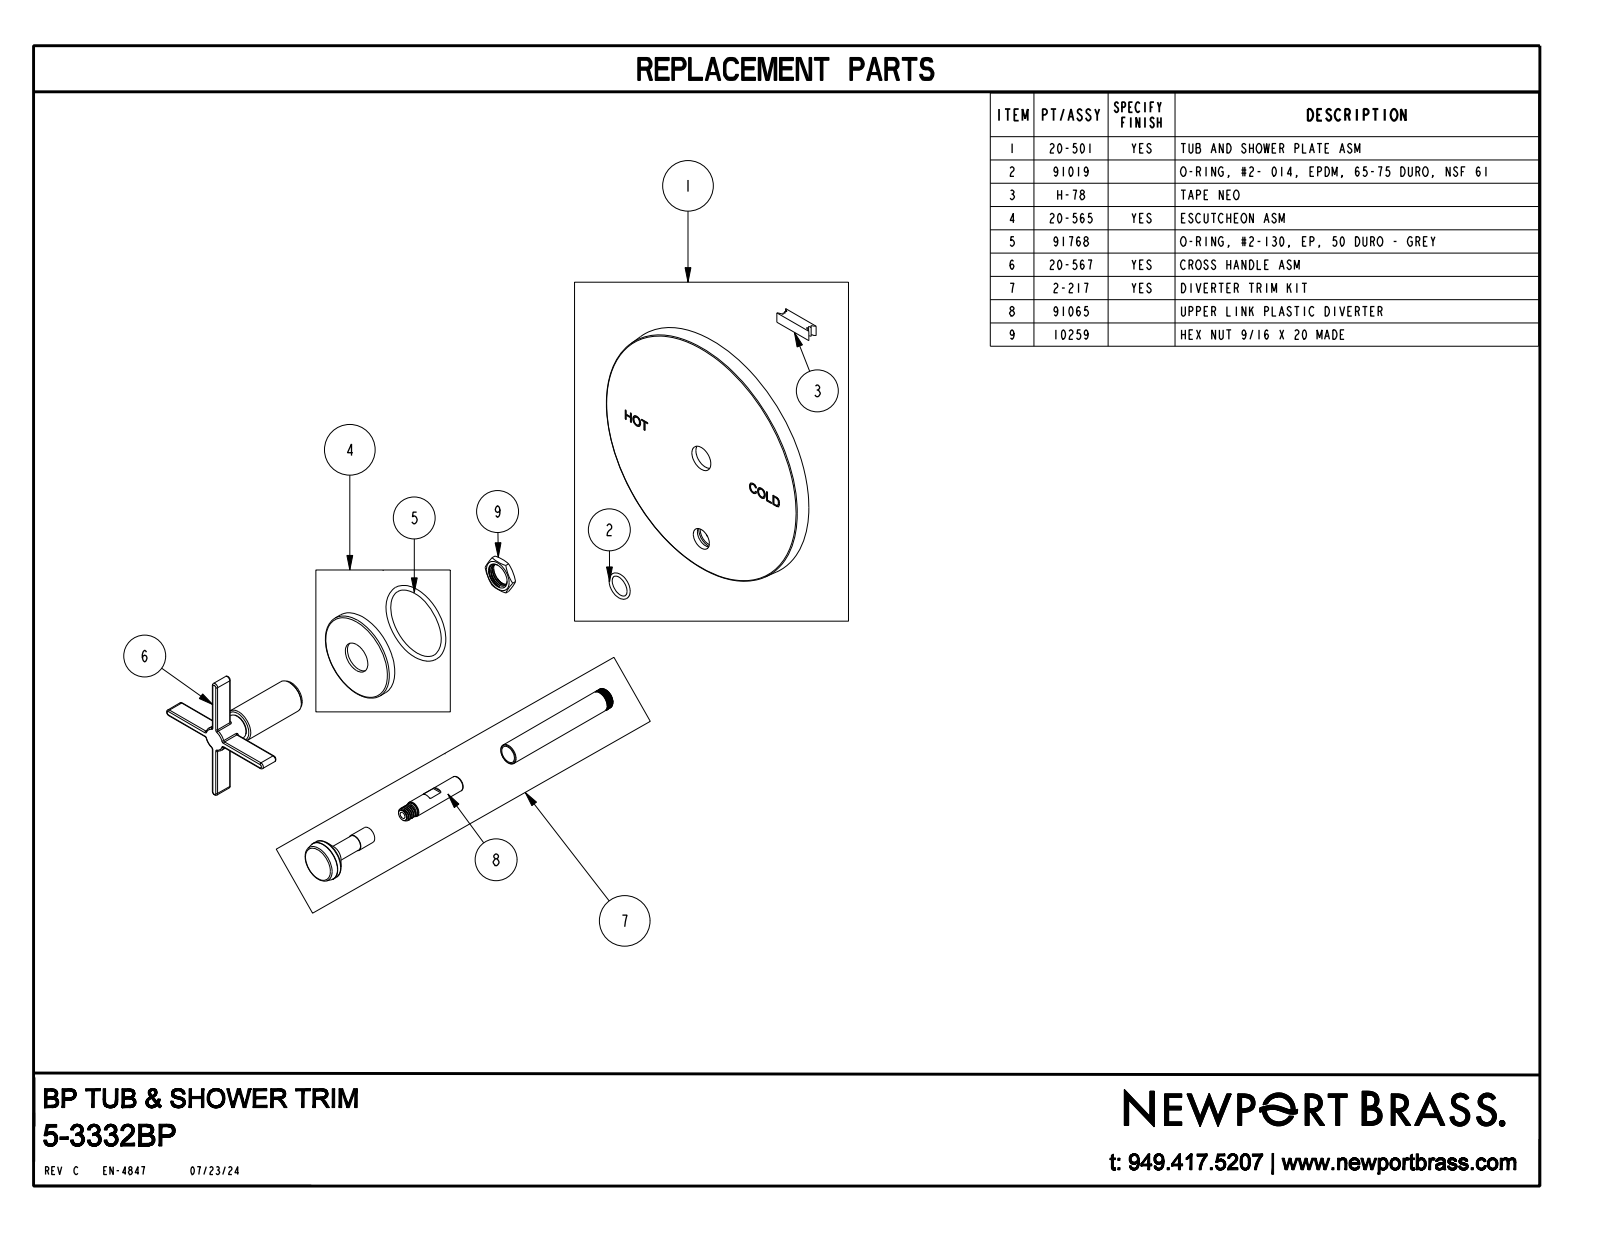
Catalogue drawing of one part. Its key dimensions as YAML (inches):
part_name: "30748; 20-501_ASM; 10497; 10496 (+8 more)"
step_written_by: "CREO PARAMETRIC BY PTC INC, 2018400 (CONFIG_CONTROL_DESIGN)"
units: inches
bodies: {solids: 7, faces: 521, planar: 131, cylindrical: 178, other: 212}
overall_size: [6, 5.994, 5.351]
volume: 5.563
surface_area: 105
round_holes:
  - {diameter: 0.6, count: 2}
  - {diameter: 0.11, count: 1}
  - {diameter: 0.265, count: 1}
  - {diameter: 0.318, count: 1}
  - {diameter: 0.345, count: 1}
  - {diameter: 0.36, count: 1}
  - {diameter: 0.397, count: 1}
  - {diameter: 0.4, count: 1}
  - {diameter: 0.5, count: 1}
  - {diameter: 0.516, count: 1}
  - {diameter: 0.535, count: 1}
  - {diameter: 0.59, count: 1}
round_bosses_or_shafts:
  - {diameter: 2, count: 1}
  - {diameter: 1.65, count: 1}
  - {diameter: 1, count: 1}
  - {diameter: 0.9, count: 1}
  - {diameter: 0.75, count: 1}
  - {diameter: 0.73, count: 1}
  - {diameter: 0.68, count: 1}
  - {diameter: 0.563, count: 1}
partial_cylinders:
  - {radius: 0.03, count: 16}
  - {radius: 0.075, count: 4}
  - {radius: 0.137, count: 1}
face_to_face_distances: [0.125, 0.225, 0.35, 0.55, 0.325, 0.2, 0.05, 0.15, 0.5, 0.275]
hole_center_spacings: [2.17]
